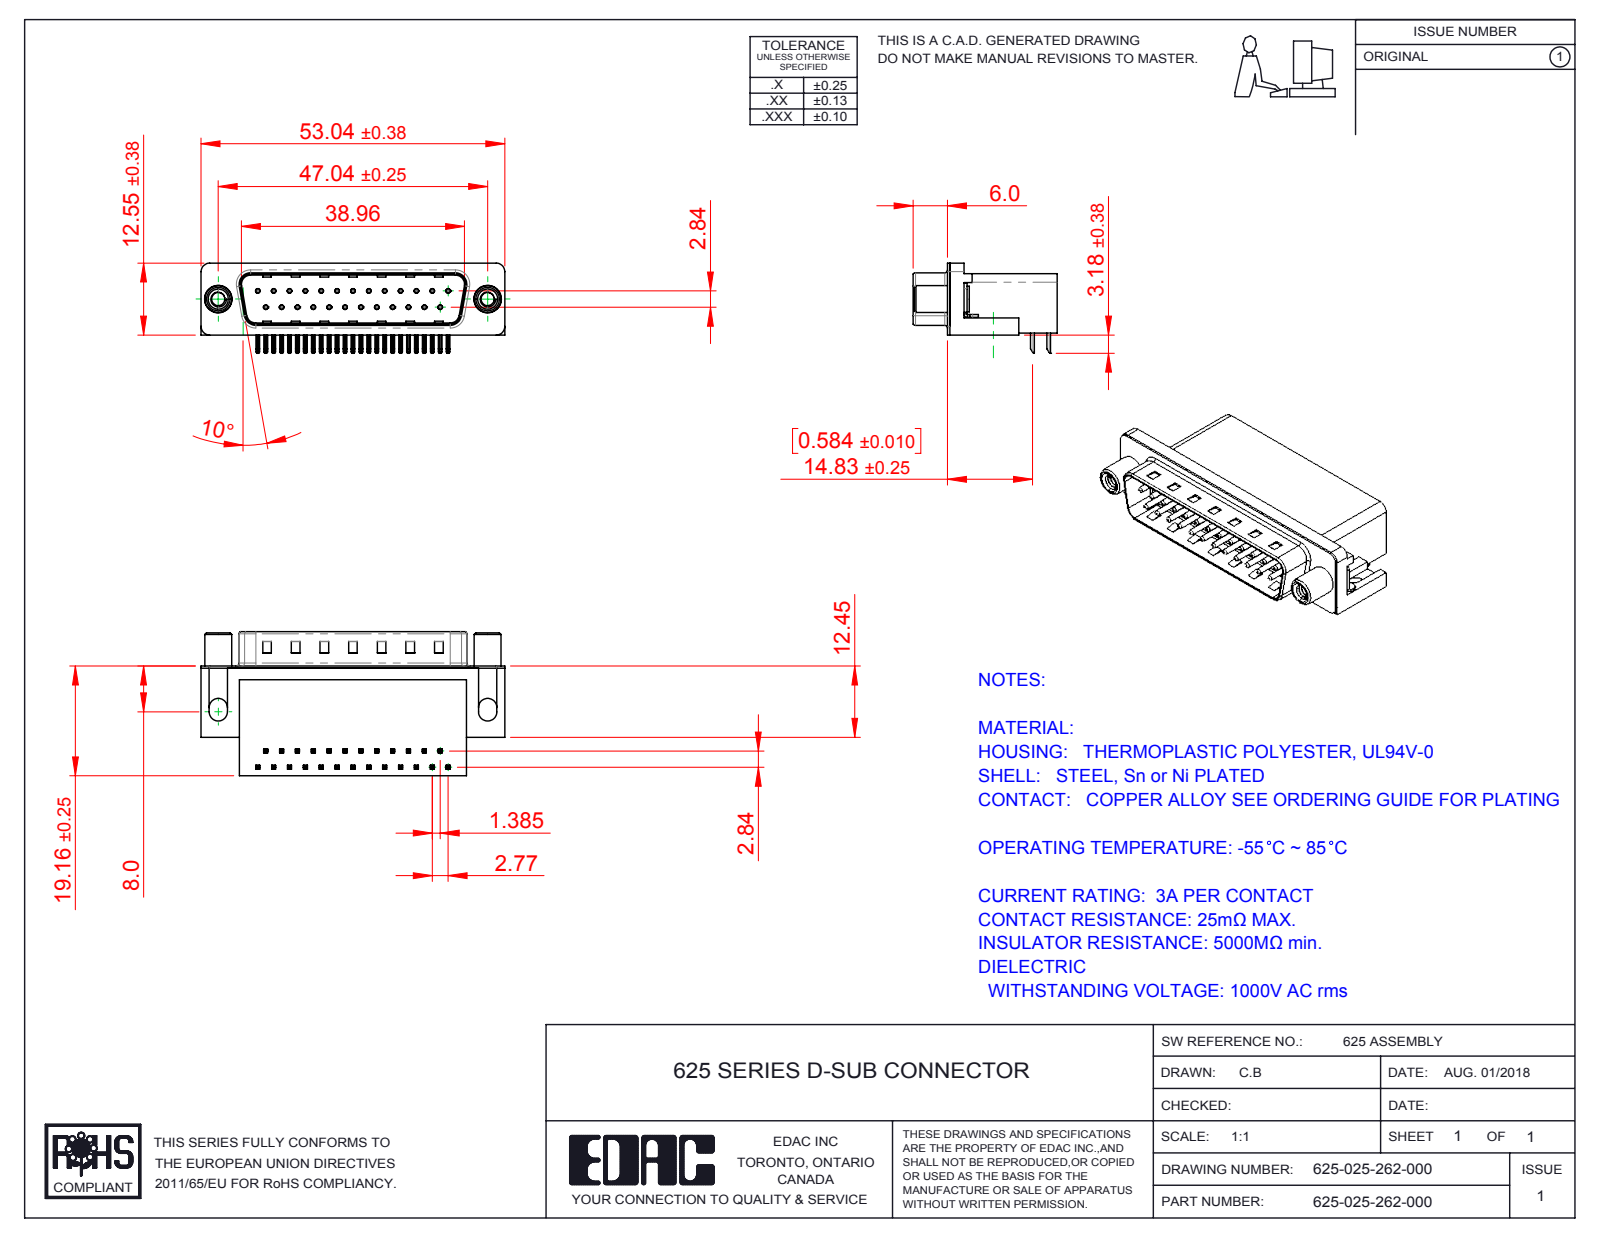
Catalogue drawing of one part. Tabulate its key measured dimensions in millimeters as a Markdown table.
| quantity | value |
| --- | --- |
| part name | 625 Round Threaded Standoff; 625 Shell_25 Socket; 625 Non Board Mount; 625 Contact Bottom (+3 more) |
| STEP written by | SolidWorks 2016 (CONFIG_CONTROL_DESIGN) |
| units | millimeters |
| bodies | 31 solids, 2257 faces (1399 planar, 665 cylindrical, 193 other) |
| overall size | 53.04 × 25.16 × 15.73 |
| volume | 9 227 mm³ |
| surface area | 8 927 mm² |
| round holes (diameter × count) | 0.35 × 25, 0.8 × 25, 2.3 × 2, 3.1 × 2, 4 × 2, 4.8 × 2, 5 × 2 |
| round bosses / shafts (diameter × count) | 0.75 × 25, 4.9 × 2, 4.7 × 2, 4.5 × 2, 3.85 × 2 |
| partial cylindrical surfaces (radius × count) | 0.25 × 100, 0.12 × 50, 1 × 16, 0.5 × 9, 1.6 × 8, 1.5 × 7, 0.9 × 4, 2 × 4 |
| main face-to-face distances | 0.4, 10.35, 18.76, 2.1, 8.76, 10.46, 10.86, 1.7, 19.16, 2.9 |
| hole center spacings | 3.16, 2.77, 11.08, 5.54, 8.31, 5.03, 13.85, 7.48 |
